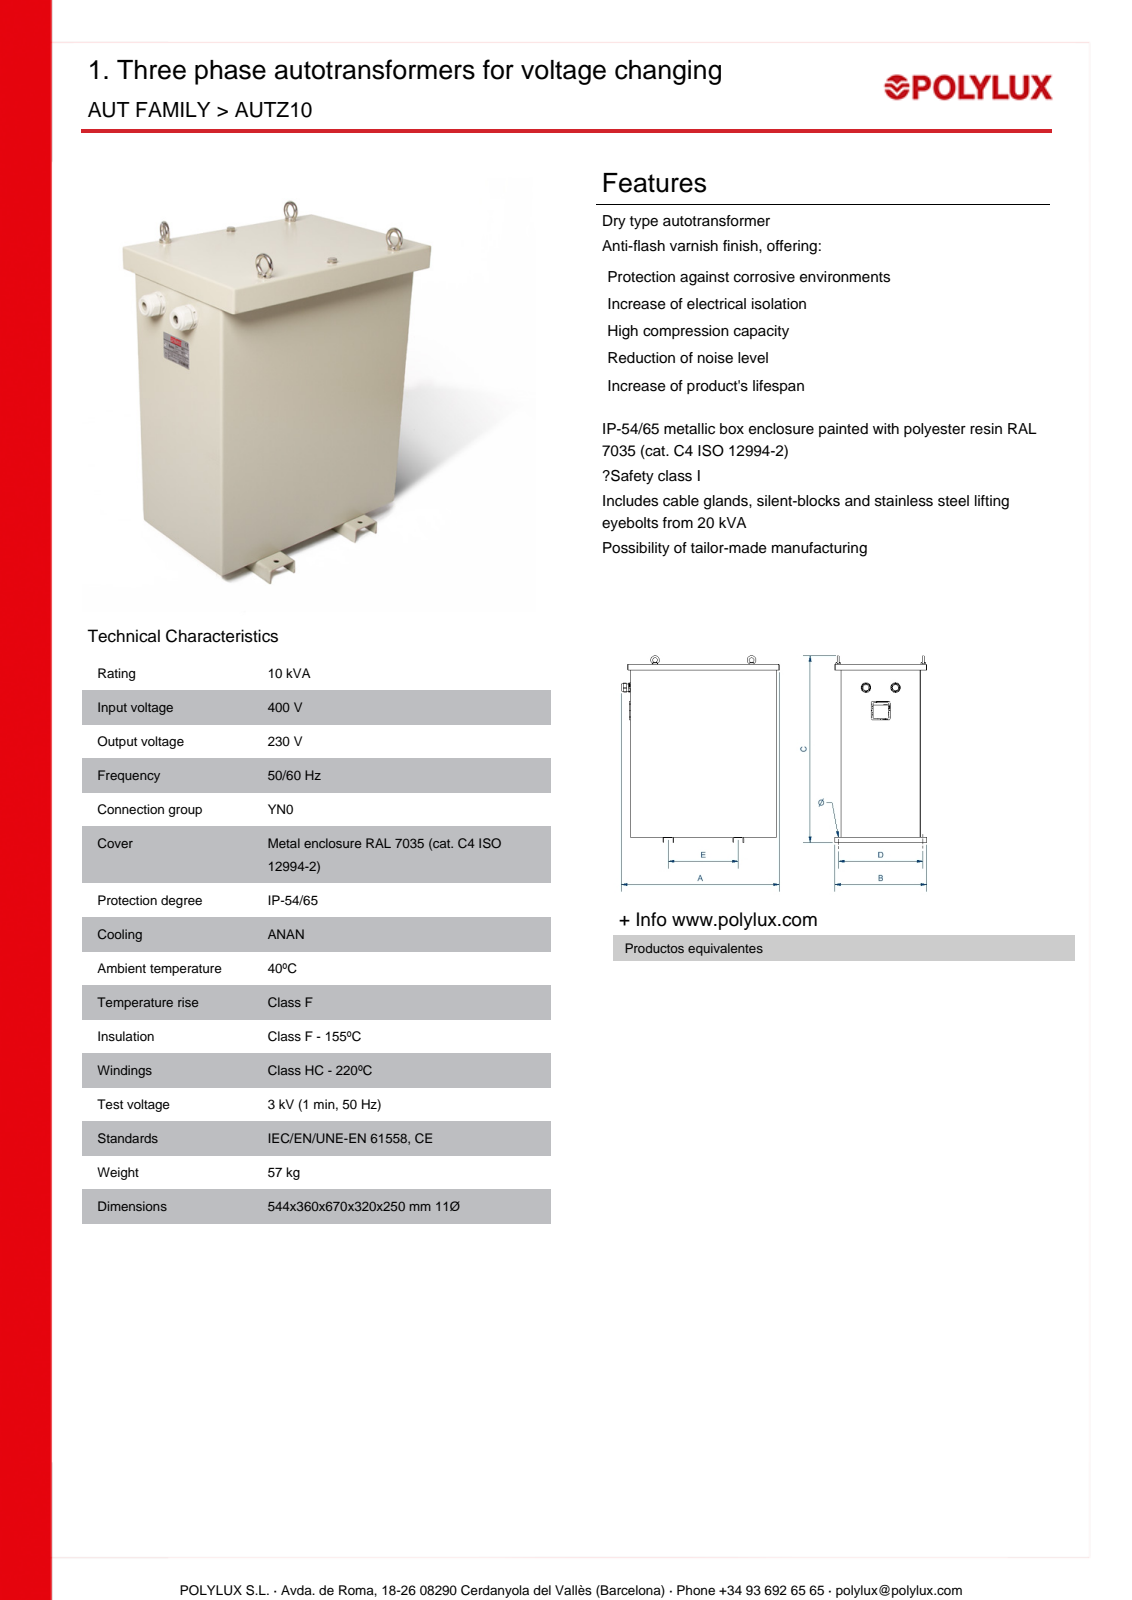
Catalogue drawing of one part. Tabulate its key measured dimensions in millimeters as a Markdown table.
| quantity | value |
| --- | --- |
| part name | CAJ14C54 |
| STEP written by | Autodesk Inventor 2018 (AUTOMOTIVE_DESIGN) |
| units | millimeters |
| bodies | 27 solids, 778 faces (428 planar, 166 cylindrical, 184 other) |
| overall size | 684 × 547.5 × 362 |
| volume | 3 148 000 mm³ |
| surface area | 3 042 000 mm² |
| round holes (diameter × count) | 11 × 8, 12 × 6, 8.38 × 4, 10.85 × 4, 11.2 × 4, 3.5 × 2, 4 × 2, 13.3 × 2, 25 × 2, 29 × 2, 32.4 × 2, 38 × 2 |
| round bosses / shafts (diameter × count) | 45 × 4, 20 × 4, 10 × 4, 9 × 4, 36.5 × 2, 35 × 2, 25.4 × 2, 17.2 × 2 |
| partial cylindrical surfaces (radius × count) | 4 × 15, 2 × 12, 5 × 8, 3 × 4, 6 × 4, 12.5 × 4 |
| main face-to-face distances | 2, 280, 498, 607, 278, 282, 605, 609, 500, 496 |
| hole center spacings | 50, 167, 250, 254.95, 270, 356.53, 367.97, 315 |
